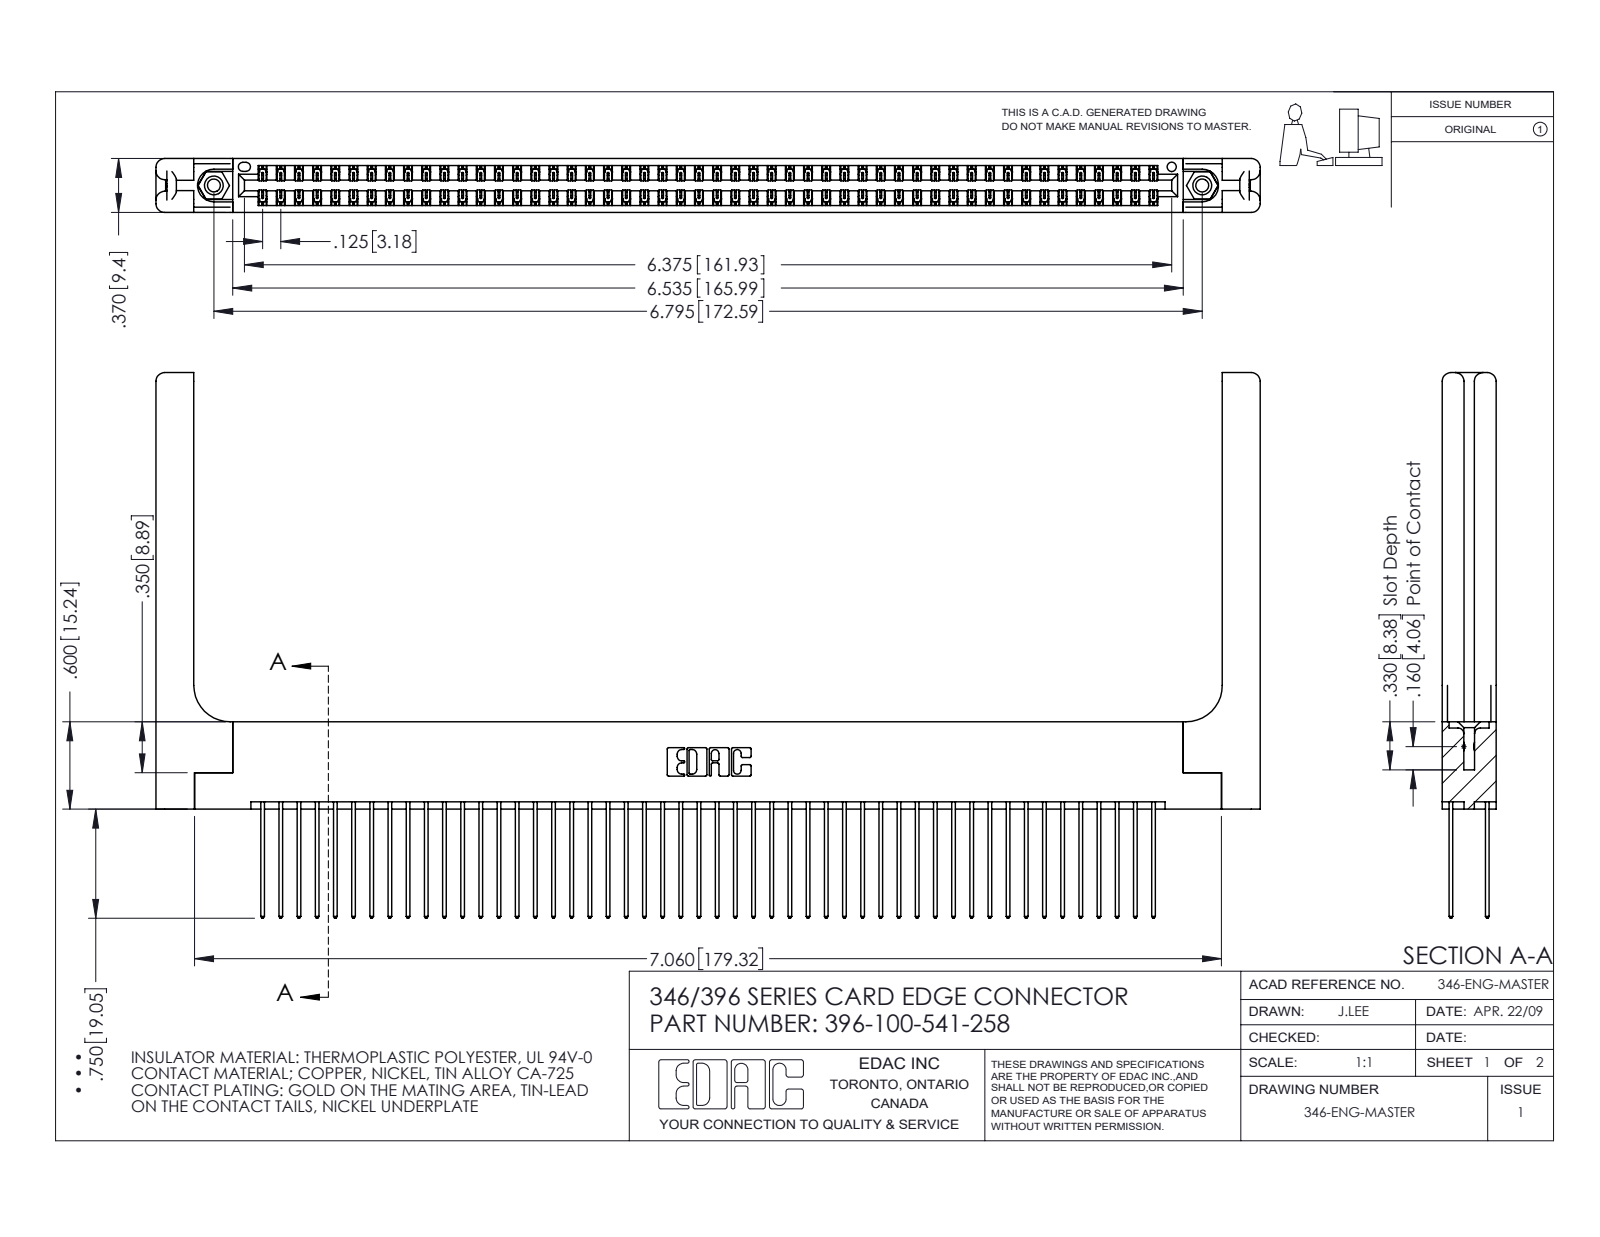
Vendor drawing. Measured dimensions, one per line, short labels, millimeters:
name: 345-292-001_345-293-141; 396-100-541-258; 345-250-001_345-250-001-102; 346 Part_Flush Mounting Lugs - 0.156 Dia-TH (+1 more)
written by: SolidWorks 2016 (CONFIG_CONTROL_DESIGN)
unit: mm
bodies: 105 solids, 5578 faces (3724 planar, 1794 cylindrical, 60 other)
size: 192.8 × 95.3 × 9.4
volume: 26 920 mm³; area: 34 570 mm²
holes: 2× ⌀2.3, 2× ⌀3.2, 2× ⌀4, 1× ⌀1.6
bosses: 2× ⌀3.9
rounds: 150× R0.2, 100× R0.3, 22× R0.3, 16× R1.5, 6× R0.2, 6× R0.8, 3× R0.7, 2× R0.4
face distances: 1.2, 8.2, 1.8, 9.4, 6.4, 0.6, 7.6, 7, 3.8, 3.8
hole spacings: 6.2, 167.3, 172.6
